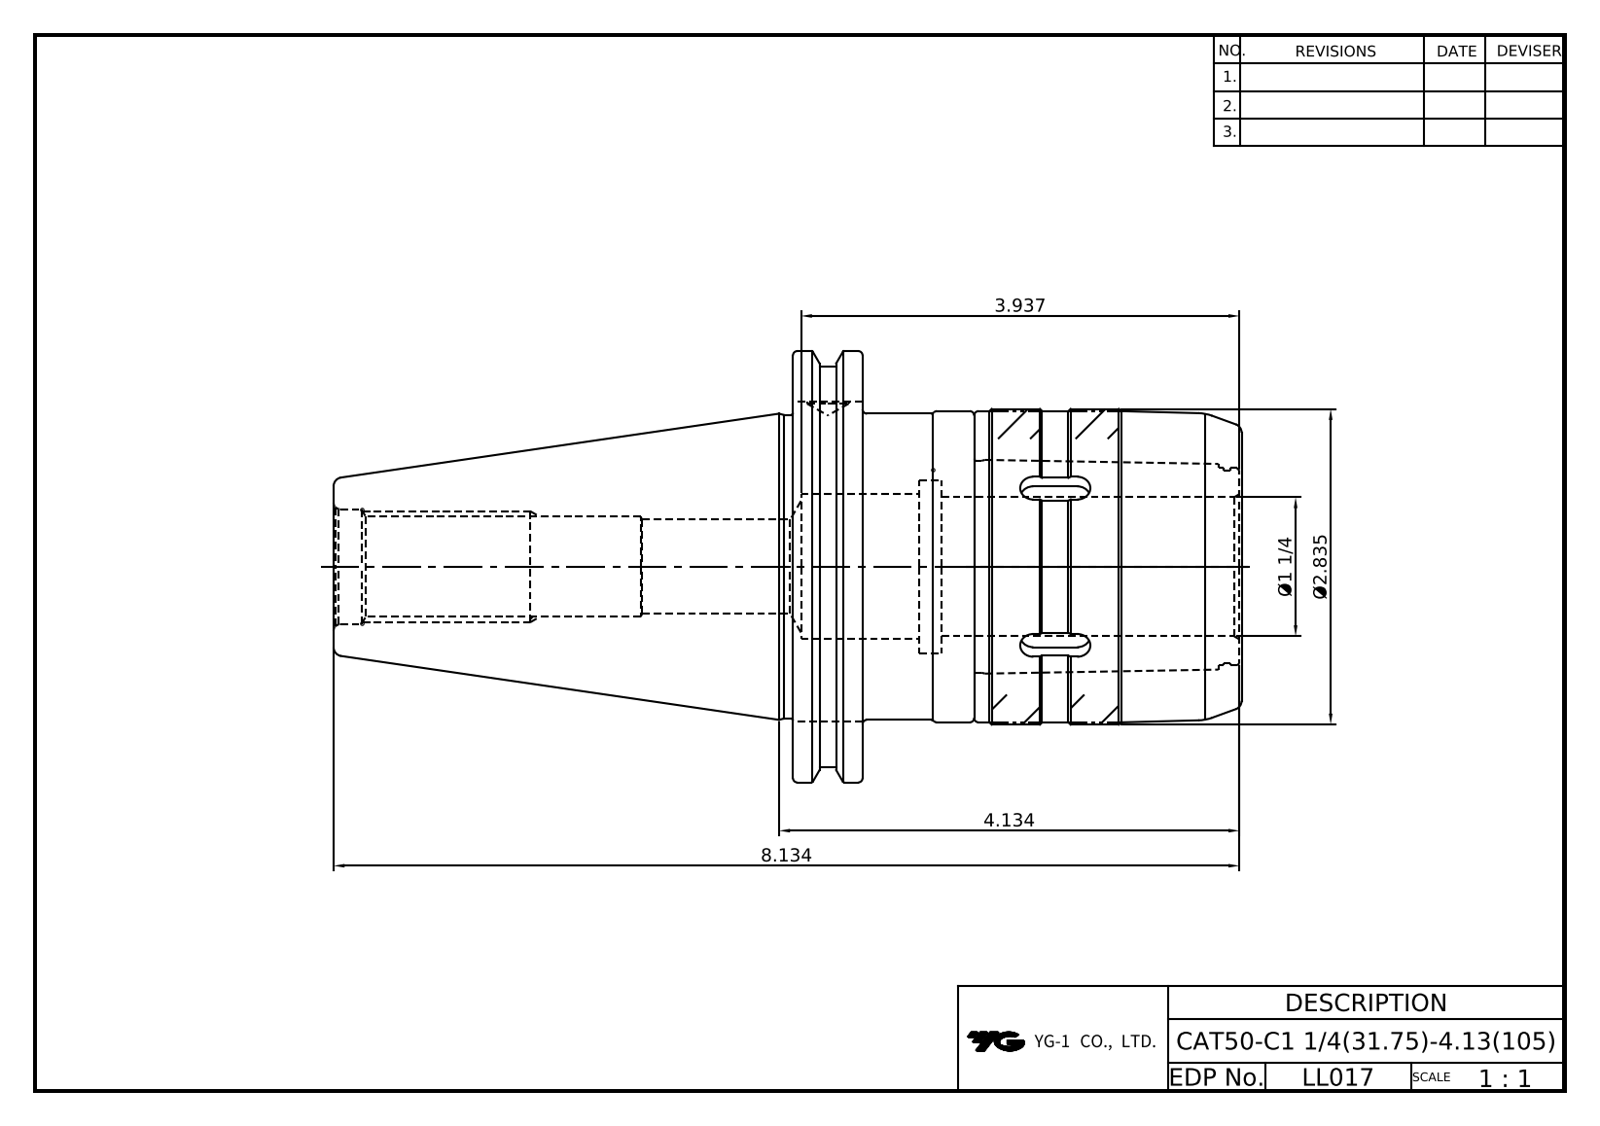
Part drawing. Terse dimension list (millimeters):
name: LL017-CAT50-C31_75-105; C32_4CAP; LL017-CAT50-C31_75-105_ASM
written by: PRO/ENGINEER BY PARAMETRIC TECHNOLOGY CORPORATION, 2012130 (CONFIG_CONTROL_DESIGN)
unit: mm
bodies: 2 solids, 234 faces (72 planar, 70 cylindrical, 92 other)
size: 207.1 × 98.4 × 94.93
volume: 556 414 mm³; area: 97 047 mm²
holes: 1× ⌀9.53, 1× ⌀21.5, 1× ⌀22.8, 1× ⌀26.19, 1× ⌀31.75, 1× ⌀33, 1× ⌀39.5, 1× ⌀56, 1× ⌀58
bosses: 1× ⌀98.4, 1× ⌀91.29, 1× ⌀72, 1× ⌀71, 1× ⌀69.85, 1× ⌀69.24, 1× ⌀49.4, 1× ⌀48.3
rounds: 10× R3
face distances: 41.32, 15.87, 25.45, 102.32, 86.45, 61, 101.82, 85.95, 60.5, 0.5
